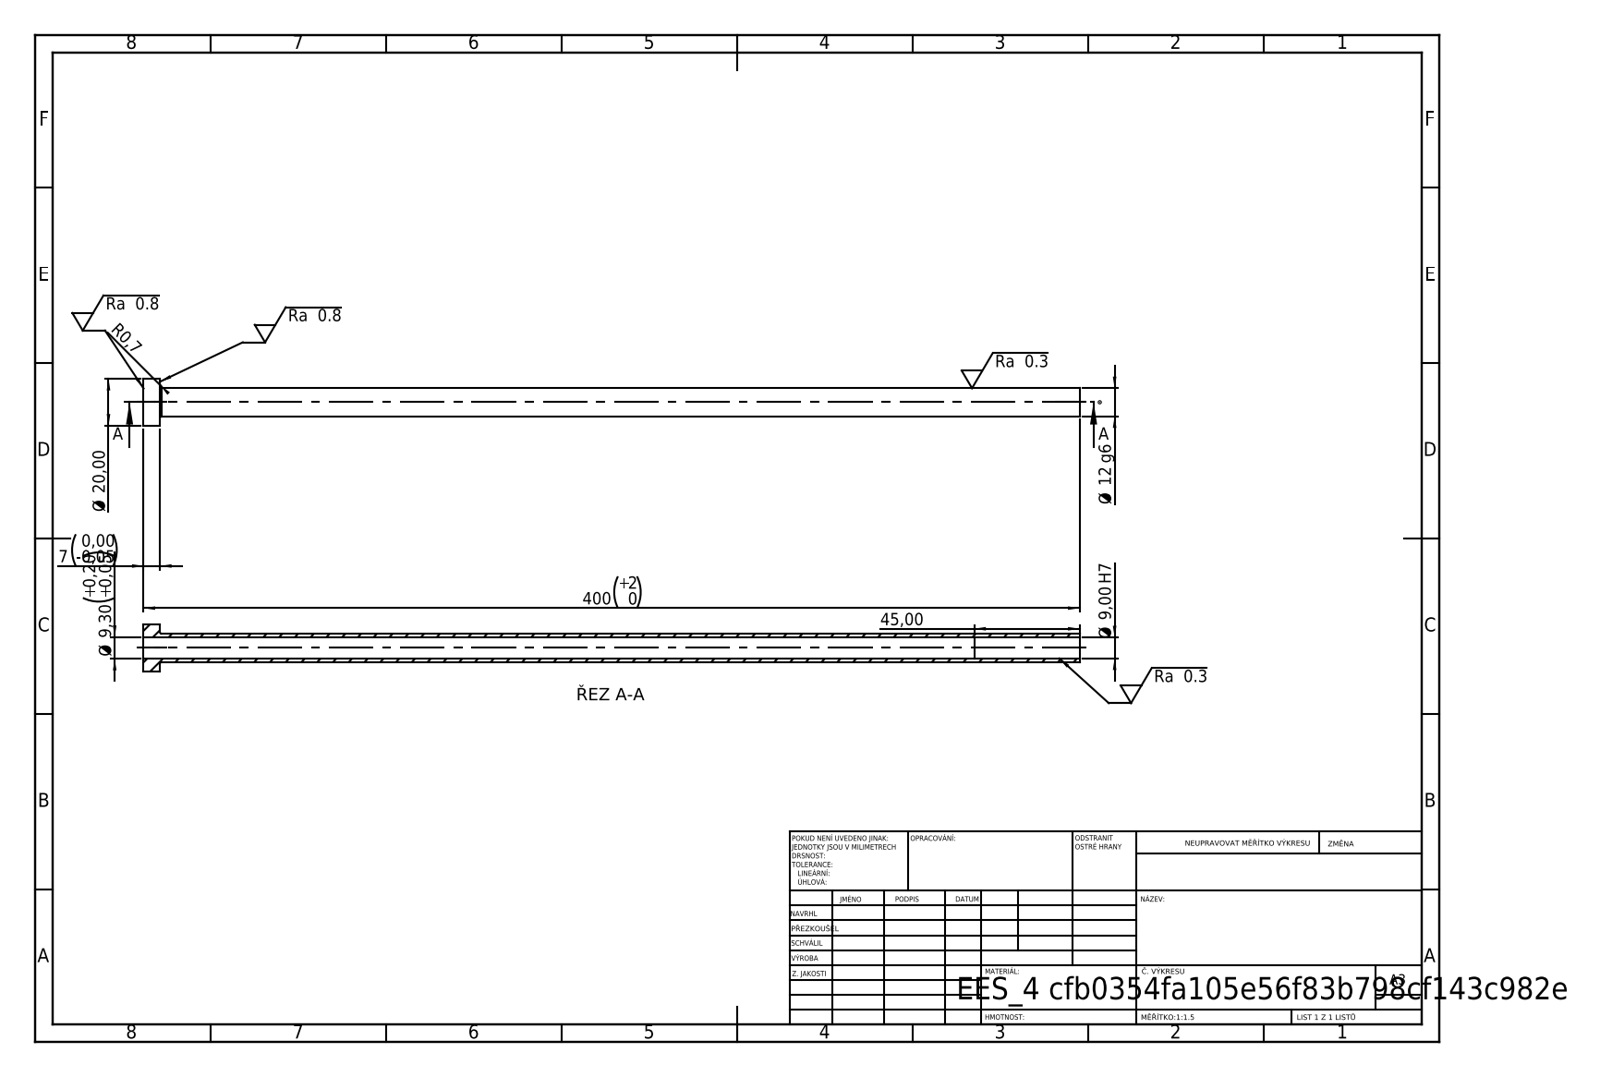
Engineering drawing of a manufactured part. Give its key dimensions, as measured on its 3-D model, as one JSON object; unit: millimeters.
{"step_written_by": "SolidWorks 2019 (CONFIG_CONTROL_DESIGN)", "units": "millimeters", "bodies": {"solids": 1, "faces": 14, "planar": 4, "cylindrical": 8, "other": 2}, "overall_size": [400, 20, 20], "volume_mm3": 19673, "surface_area_mm2": 27390, "round_holes": [[9, 1], [9.3, 1]], "round_bosses_or_shafts": [[20, 1], [12, 1]], "face_to_face_distances": [7, 400, 393, 355, 348, 45]}
